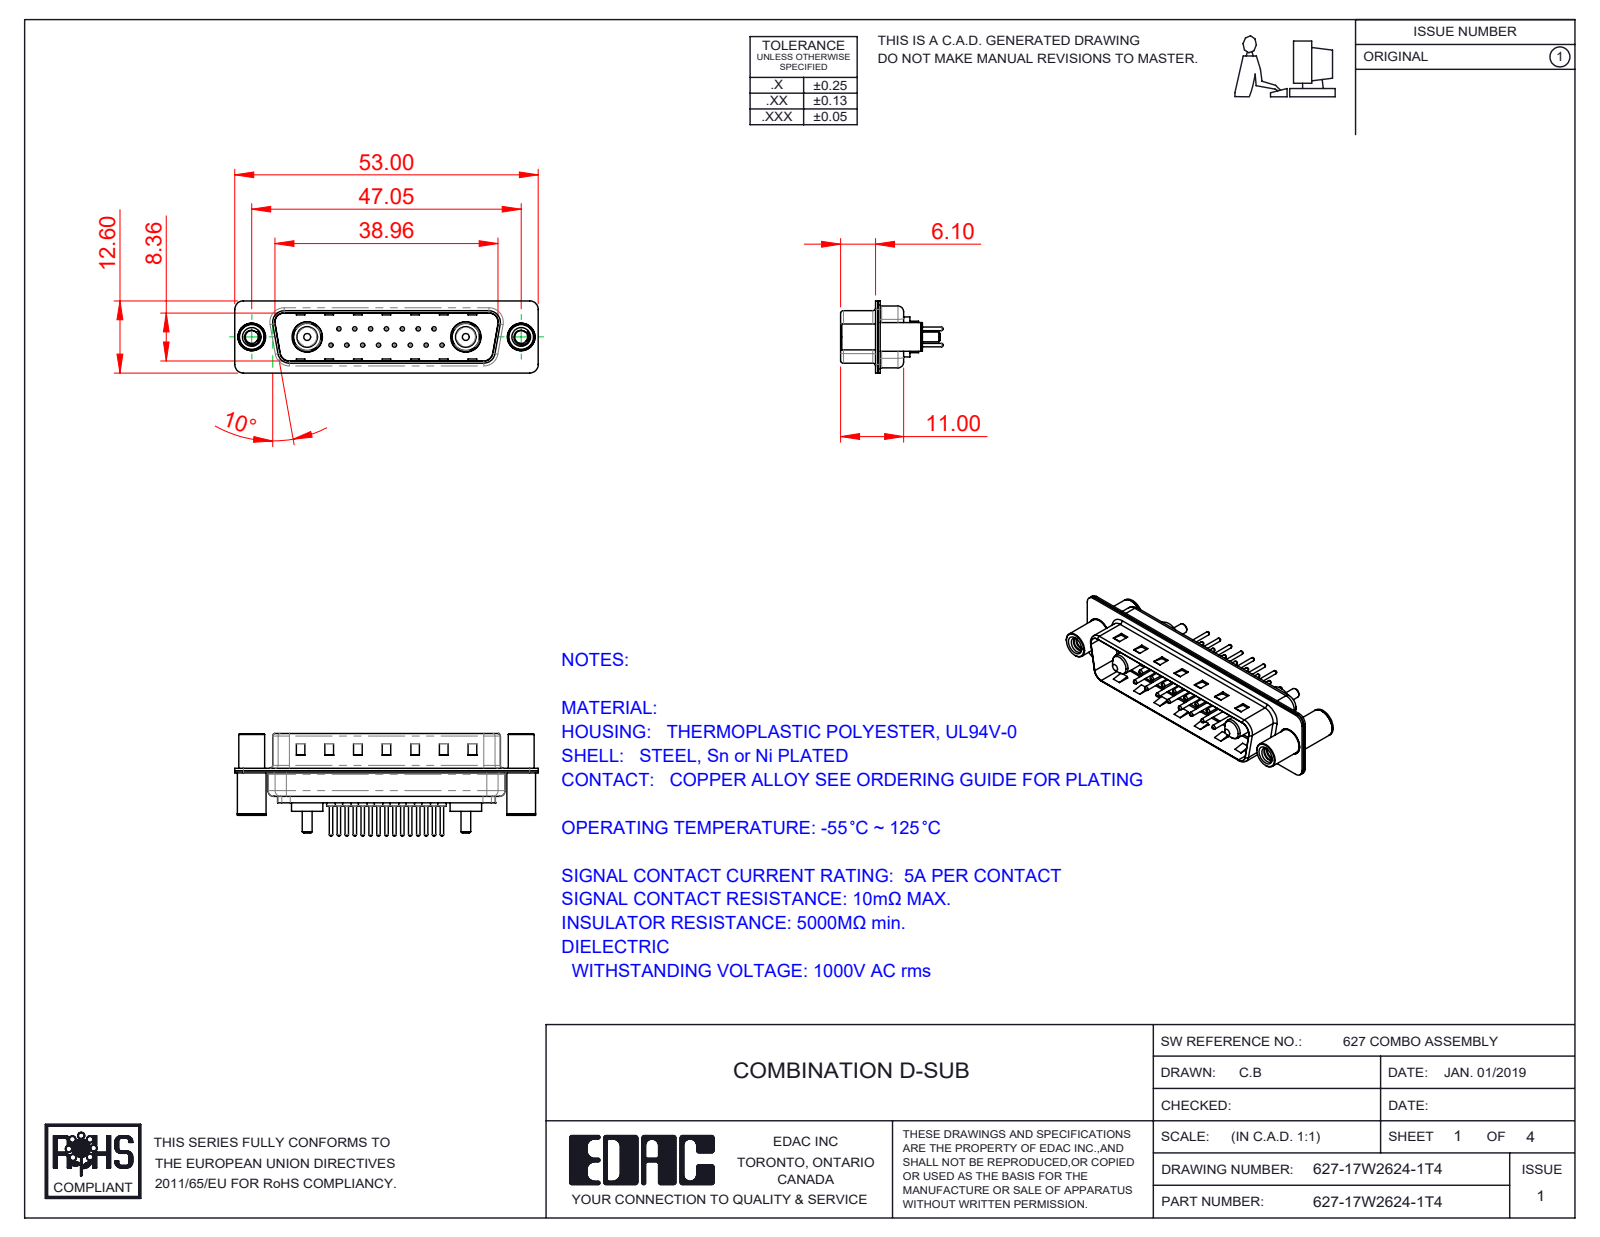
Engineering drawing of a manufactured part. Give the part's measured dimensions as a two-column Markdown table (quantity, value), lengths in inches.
| quantity | value |
| --- | --- |
| part name | 627Combo Contact Row 1_24; 627Combo Threaded Standoff and Board Spacer_4; 627-17W2624-1T4; 627Combo Shell Front_25 Contacts (+4 more) |
| STEP written by | SolidWorks 2016 (CONFIG_CONTROL_DESIGN) |
| units | inches |
| bodies | 24 solids, 1097 faces (302 planar, 437 cylindrical, 358 other) |
| overall size | 2.087 × 0.705 × 0.496 |
| volume | 0.19 in³ |
| surface area | 11.3 in² |
| round holes (diameter × count) | 0.03 × 15, 0.063 × 15, 0.079 × 15, 0.089 × 2, 0.128 × 2, 0.157 × 2, 0.189 × 2, 0.191 × 2, 0.209 × 2 |
| round bosses / shafts (diameter × count) | 0.059 × 15, 0.024 × 15, 0.217 × 2, 0.205 × 2, 0.197 × 2, 0.193 × 2, 0.187 × 2, 0.177 × 2 |
| partial cylindrical surfaces (radius × count) | 0.059 × 16, 0.079 × 12, 0.02 × 8, 0.063 × 8, 0.01 × 4, 0.024 × 4, 0.026 × 4, 0.035 × 4 |
| main face-to-face distances | 0.016, 0.032, 0.377, 0.345, 0.059, 0.22, 0.236, 0.205, 0.031, 0.048 |
| hole center spacings | 0.124, 0.109, 0.218, 0.327, 0.198, 0.295, 0.436, 0.198 |
